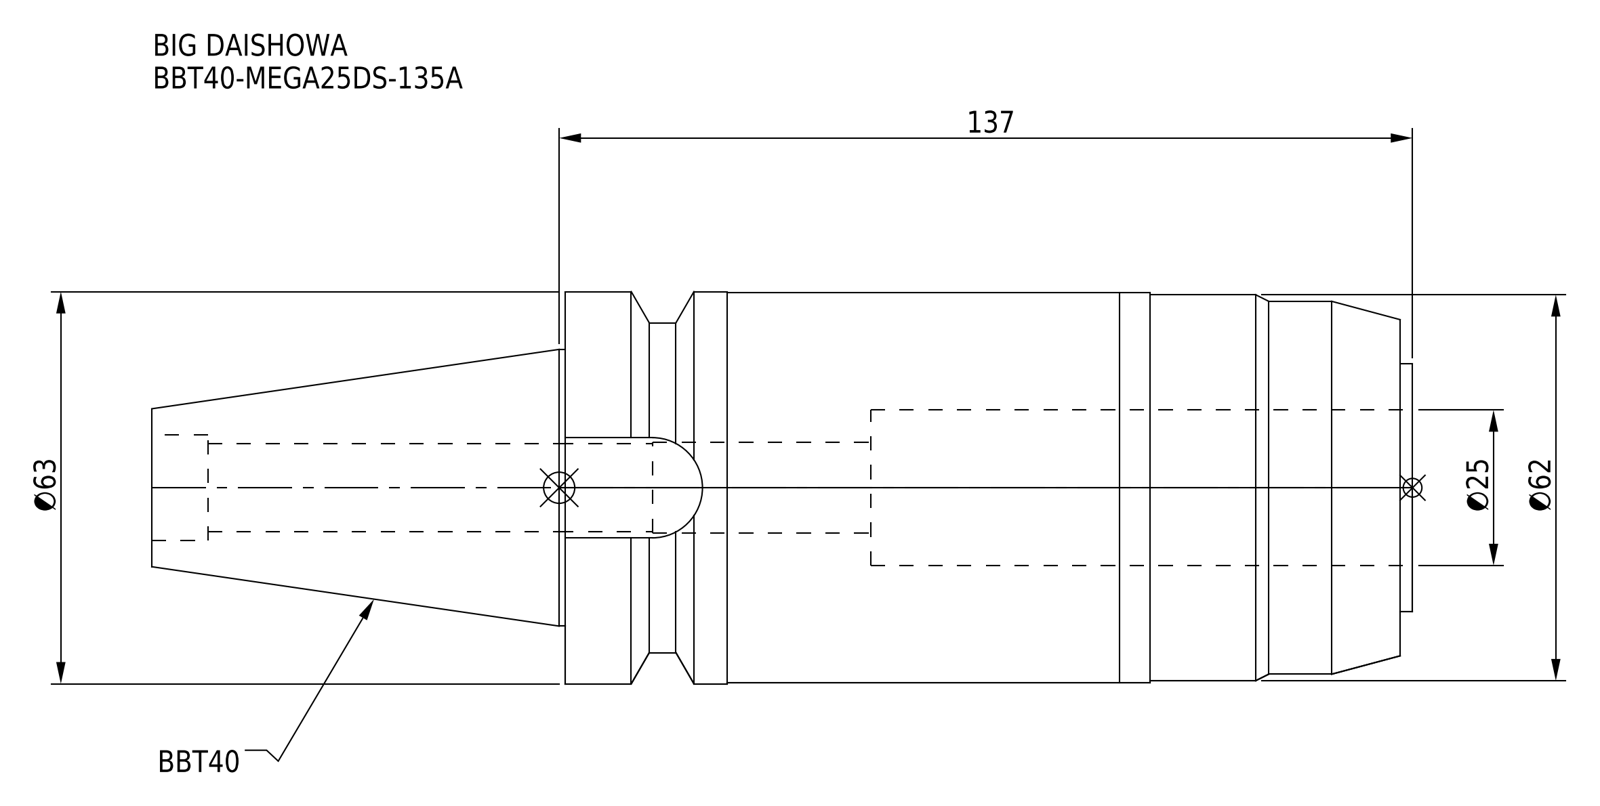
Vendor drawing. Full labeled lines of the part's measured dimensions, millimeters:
Part name (STEP PRODUCT): BBT40-MEGA25DS-135A
STEP written by: CREO PARAMETRIC BY PTC INC, 2016380 (AUTOMOTIVE_DESIGN)
Units: millimetres
Bodies: 1 solid, 53 faces (15 planar, 28 cylindrical, 10 other)
Overall size (bounding box): 202.4 × 63 × 63
Volume: 399 555 mm³ · Surface area: 51 165 mm²
Round holes (diameter × count): ⌀14.2 ×1, ⌀14.5 ×1, ⌀17 ×1, ⌀25 ×1
Round bosses / shafts (diameter × count): ⌀63 ×1, ⌀62.7 ×1, ⌀62 ×1, ⌀59.9 ×1, ⌀53 ×1, ⌀44.45 ×1, ⌀39.9 ×1
Partial cylindrical surfaces — rounded edges, fillets, slot ends (radius × count): R8.05 ×1
Main face-to-face distances: 134, 2, 136, 45, 87, 85, 49, 202.4, 200.4, 115.4
